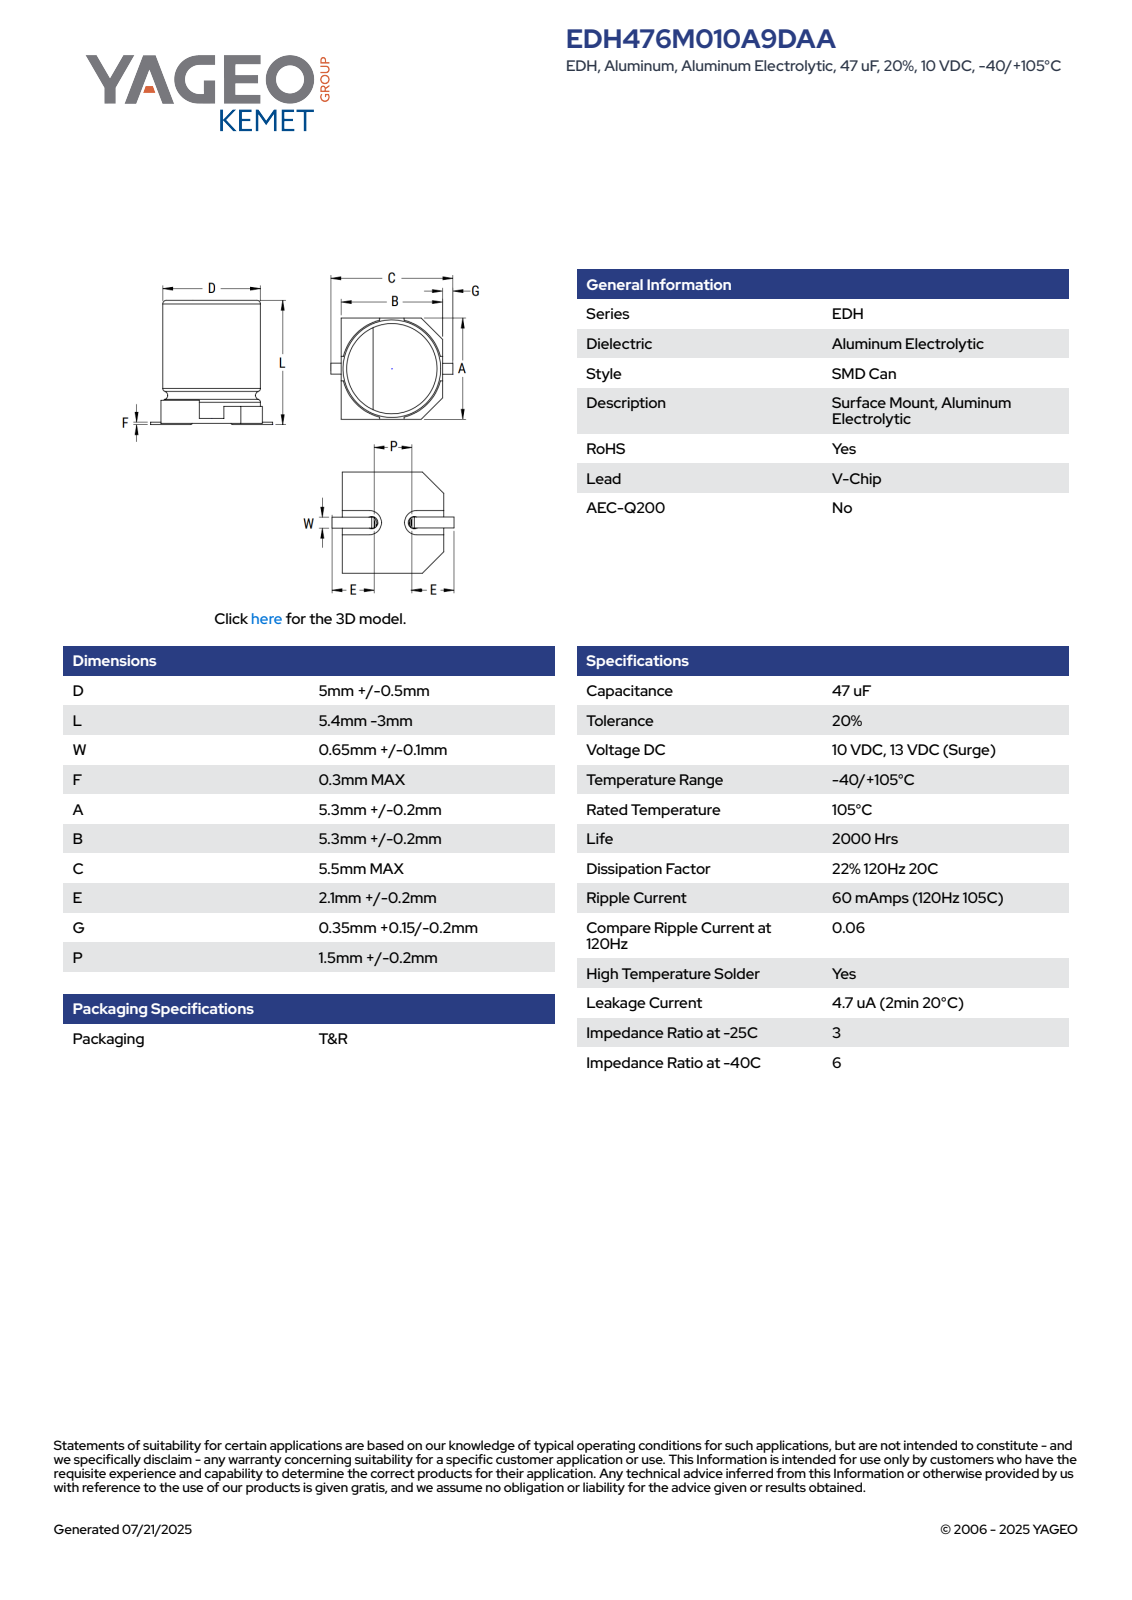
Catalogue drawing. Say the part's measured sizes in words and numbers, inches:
The part is named "CAC_S_5X5.4_D5.5L5.65W0.75F0.3A5.5B5.5C5.5E2.4P1.7". Its 3-D file was written by "SolidWorks 2014 (AUTOMOTIVE_DESIGN)". It is 5 solids with 78 faces: 61 planar, 11 cylindrical and 6 other. Overall it measures 0.256 by 0.223 by 0.217 inches. Its volume is 0.007 cubic inches and its surface area 0.336 square inches. Round bosses or shafts: 1 of diameter 0.207. Partial cylindrical surfaces (rounded edges, fillets, slot ends): 2 of radius 0.008, 1 of radius 0.086, 1 of radius 0.108. The main face-to-face distances are 0.211, 0.2, 0.211, 0.2, 0.217, 0.023, 0.222, 0.223, 0.067, 0.056.
